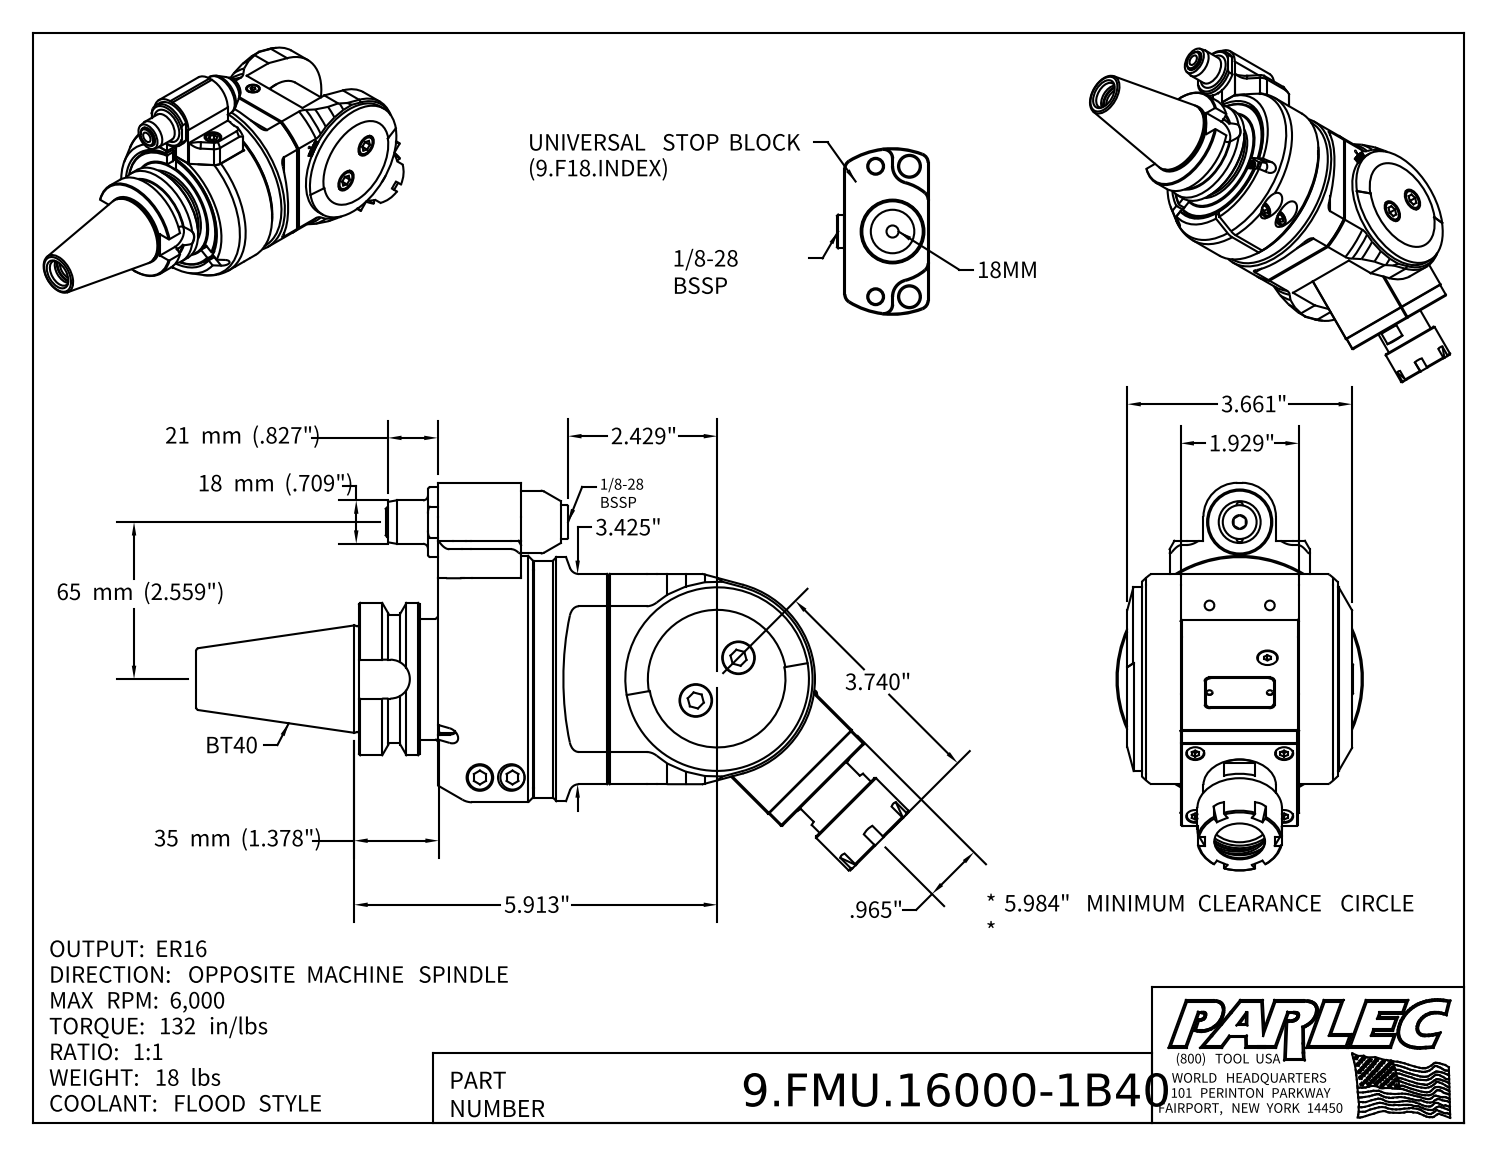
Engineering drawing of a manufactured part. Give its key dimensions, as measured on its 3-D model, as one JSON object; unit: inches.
{"part_name": "9.FMU.16000-1B40; 9_GA1_346_2 (EVO, Type 1, BT40, 65mm); 9_FMU_16000", "step_written_by": "Autodesk Inventor 2022 (AUTOMOTIVE_DESIGN)", "units": "inches", "bodies": {"solids": 6, "faces": 666, "planar": 367, "cylindrical": 141, "other": 158}, "overall_size": [11.606, 6.317, 4.016], "volume_in3": 77.11, "surface_area_in2": 306.6, "round_holes": [[0.295, 4], [0.531, 3], [0.102, 2], [0.157, 2], [0.165, 2], [0.197, 2], [0.335, 2], [0.409, 2], [0.433, 2], [1.063, 2], [0.098, 1], [0.118, 1]], "round_bosses_or_shafts": [[0.394, 4], [0.276, 4], [0.236, 4], [0.512, 3], [0.315, 3], [0.709, 2], [0.472, 2], [0.098, 2]], "partial_cylinders_radius": [[0.079, 8], [0.157, 6], [0.02, 2], [0.039, 2], [0.138, 2], [0.197, 2], [0.551, 2], [0.317, 1]], "face_to_face_distances": [0.551, 2.48, 0.315, 3.031, 1.929, 3.425, 2.795, 0.866, 3.346, 0.63], "hole_center_spacings": [1.024, 0.059, 0.276, 0.983, 1.023, 1.066, 1.189, 1.298]}
